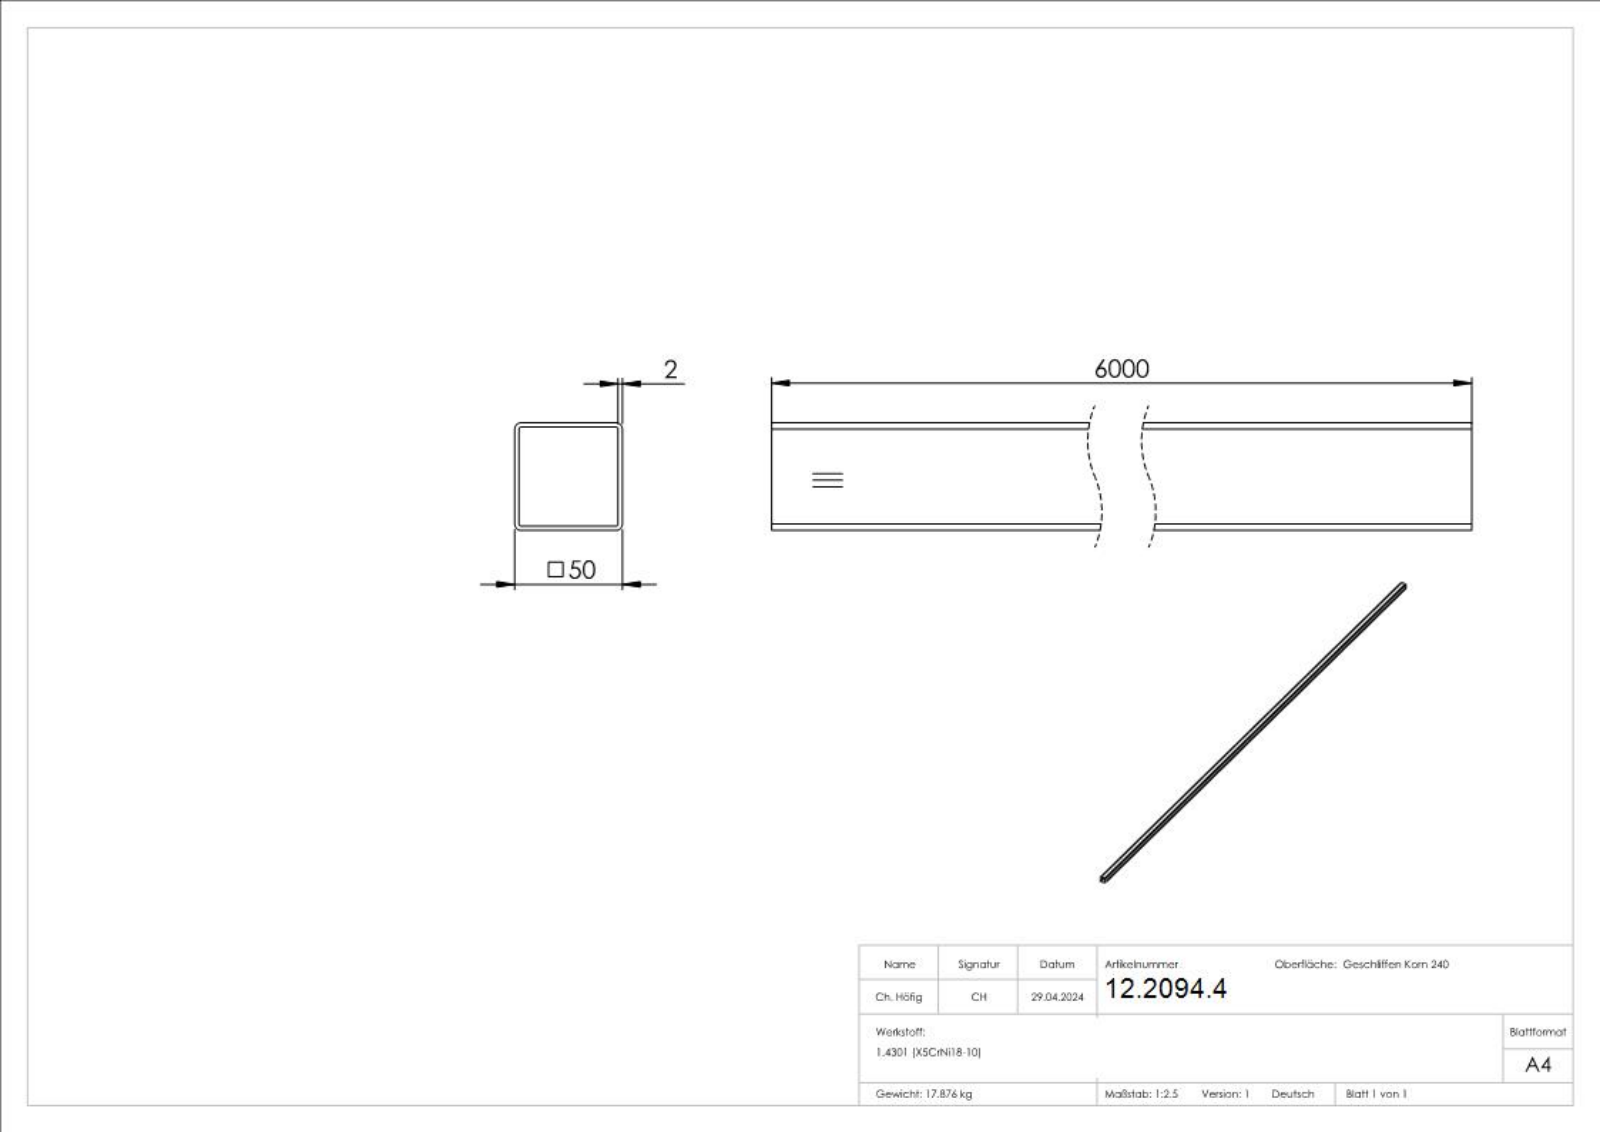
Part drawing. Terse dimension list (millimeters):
name: 55405-240
written by: SolidWorks 2018 (CONFIG_CONTROL_DESIGN)
unit: mm
bodies: 1 solid, 289 faces (165 planar, 8 cylindrical, 116 other)
size: 6000 × 50 × 50
volume: 2 263 000 mm³; area: 2 264 000 mm²
rounds: 4× R1, 4× R3
face distances: 2, 48, 50, 46, 6000, 1.9, 46.1, 48.1, 0.88, 1.82
